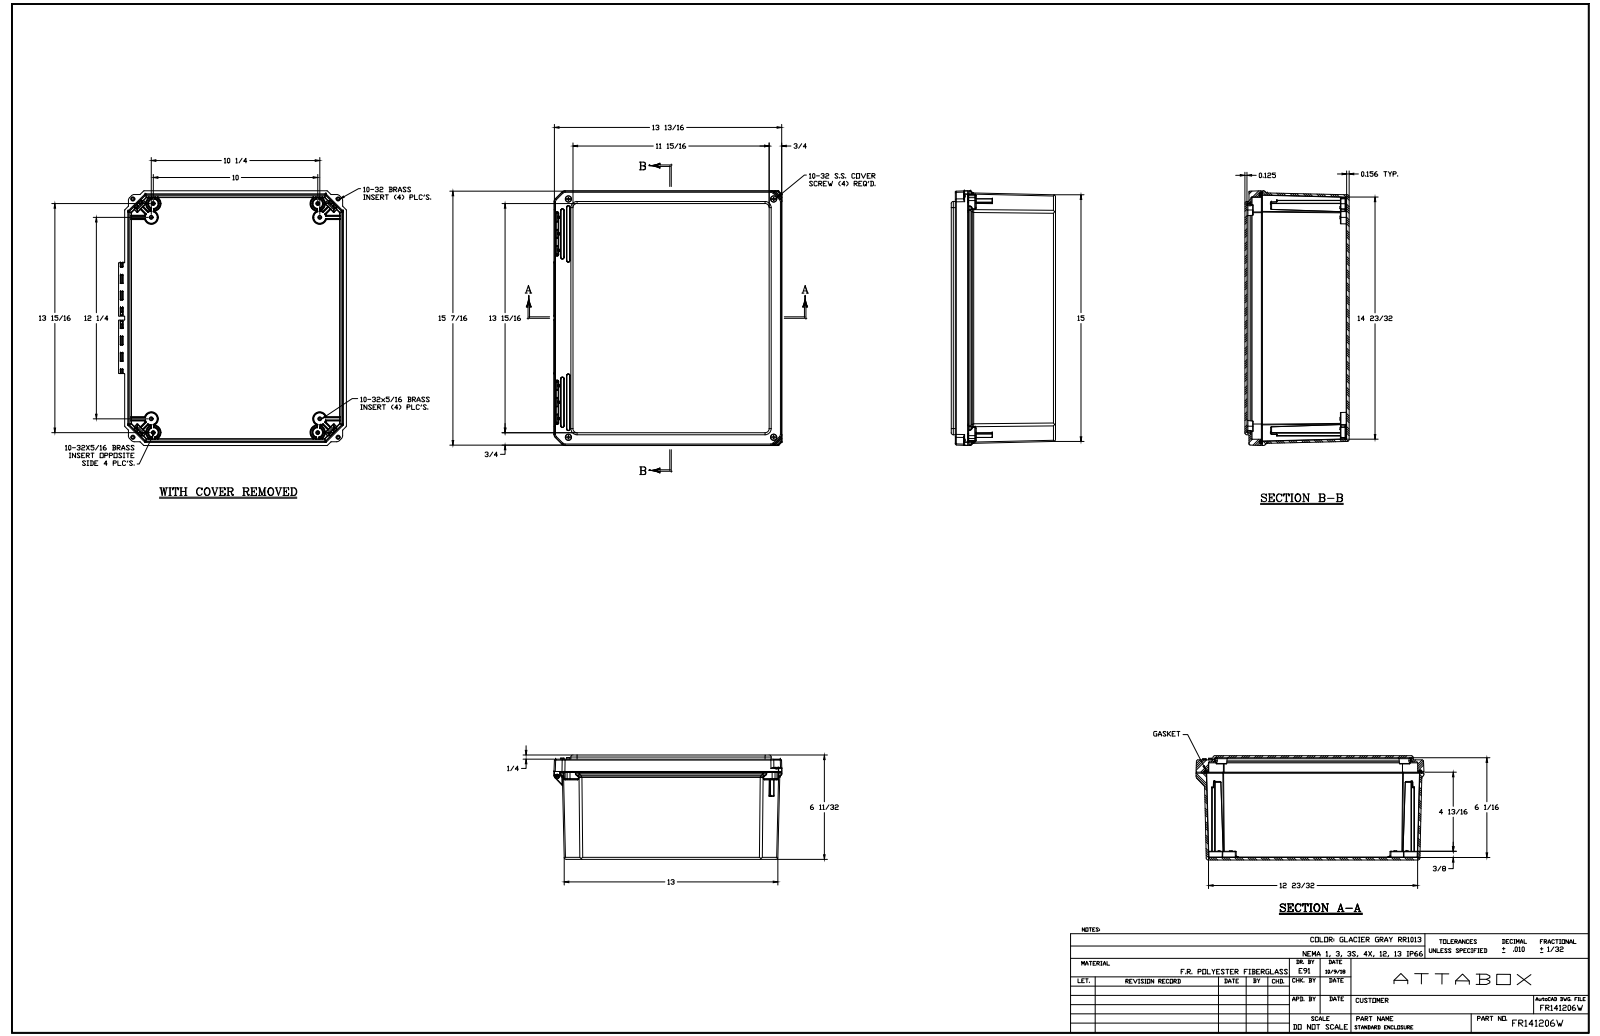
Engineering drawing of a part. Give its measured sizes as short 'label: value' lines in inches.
name: FR141206W
written by: SolidWorks 2018 (AUTOMOTIVE_DESIGN)
unit: in
bodies: 23 solids, 2137 faces (713 planar, 782 cylindrical, 642 other)
size: 15.505 × 13.865 × 6.341
volume: 120 in³; area: 1 602 in²
holes: 12× ⌀0.156, 8× ⌀0.152, 4× ⌀0.252, 4× ⌀0.253, 2× ⌀0.219, 2× ⌀0.227, 2× ⌀0.313, 1× ⌀0.137
bosses: 12× ⌀0.246, 4× ⌀0.87, 4× ⌀0.45, 4× ⌀0.199, 2× ⌀0.435
rounds: 178× R0.01, 88× R0.005, 49× R0.02, 42× R0.03, 24× R0.03, 24× R0.09, 24× R0.096, 22× R0.125
face distances: 0.156, 0.125, 6.185, 6.341, 6.217, 6.061, 0.14, 0.139, 0.25, 0.125
hole spacings: 11.425, 0.841, 1.277, 1.582, 10.16, 11.248, 13.081, 13.416
